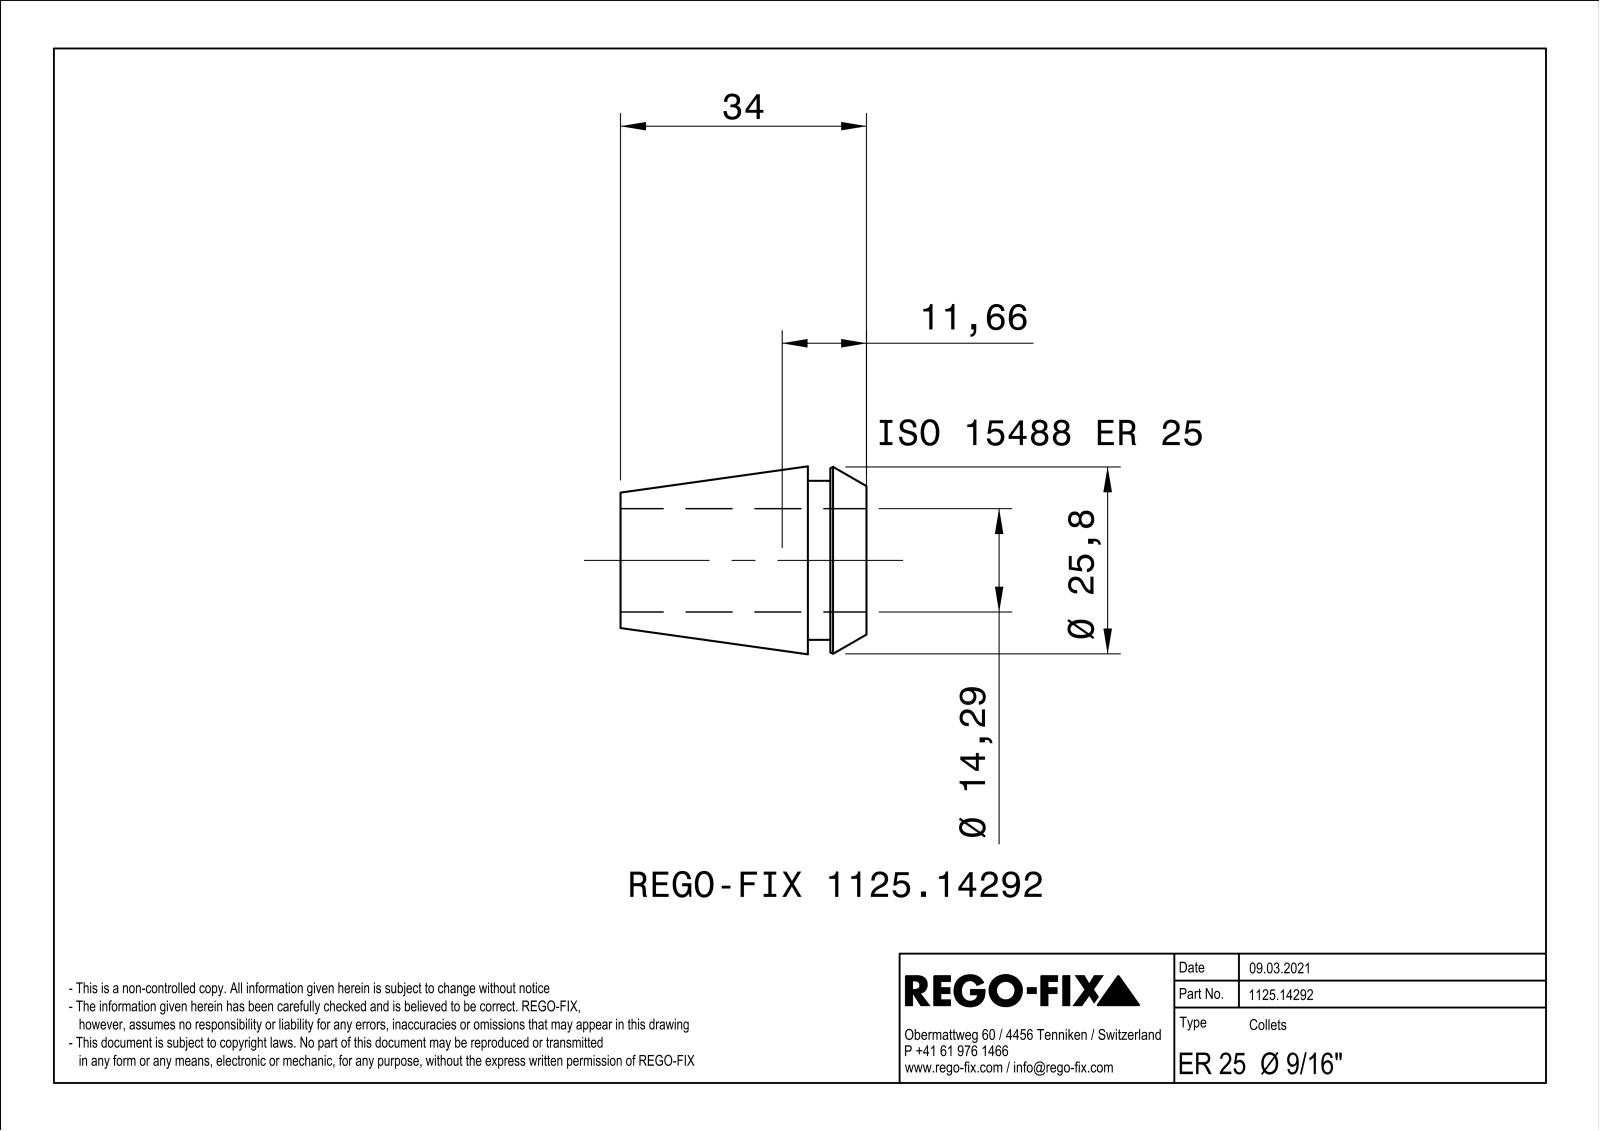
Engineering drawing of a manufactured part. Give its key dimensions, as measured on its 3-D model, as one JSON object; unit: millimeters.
{"part_name": "NOCUT", "step_written_by": "SIEMENS PLM Software Solid Edge ST10 (AUTOMOTIVE_DESIGN)", "units": "millimeters", "bodies": {"solids": 1, "faces": 177, "planar": 72, "cylindrical": 25, "other": 80}, "overall_size": [34, 25.99, 25.99], "volume_mm3": 6569, "surface_area_mm2": 7675, "round_holes": [[14.29, 1]], "round_bosses_or_shafts": [[22, 1]], "partial_cylinders_radius": [[0.4, 8]], "face_to_face_distances": [0.8, 8.1, 5, 3.1, 34, 29, 25.9]}
